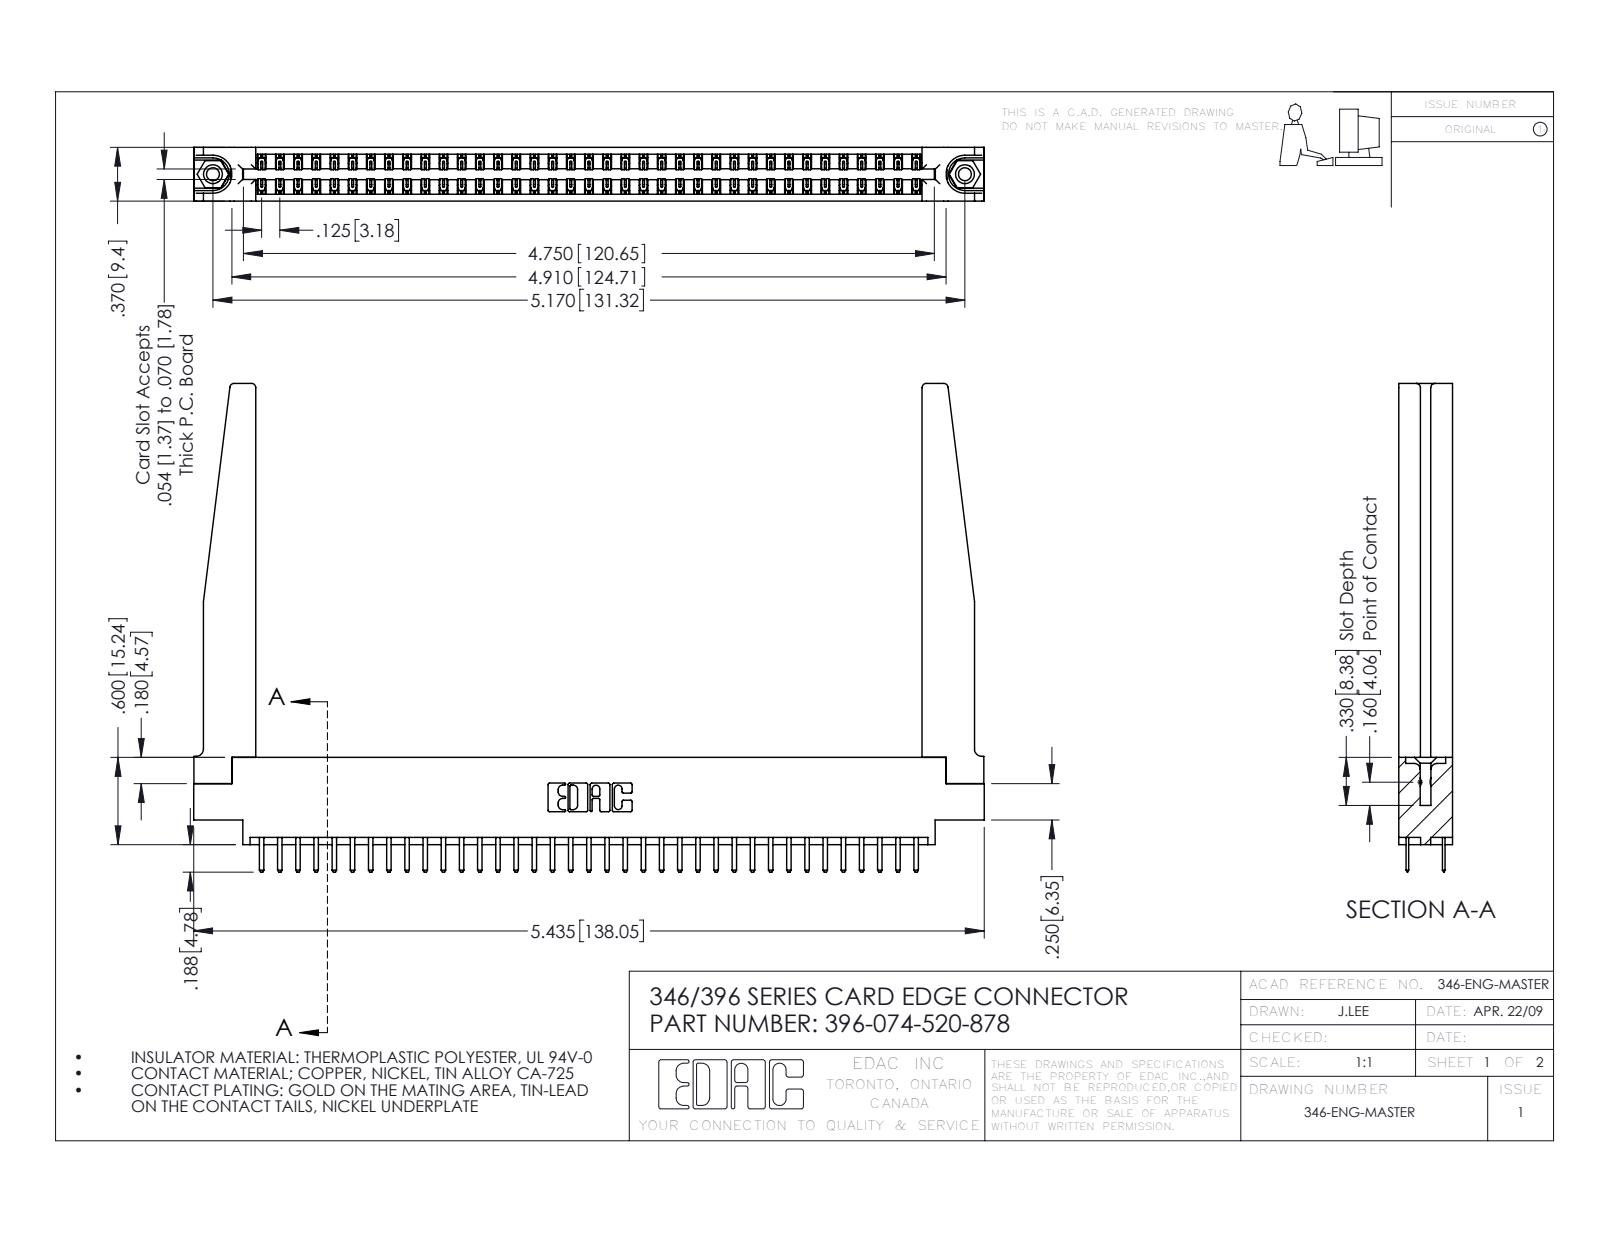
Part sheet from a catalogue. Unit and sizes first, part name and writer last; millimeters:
Units: millimetres
Overall size (bounding box): 138 × 85.3 × 9.4
Round holes (diameter × count): ⌀2.3 ×2, ⌀3.2 ×2, ⌀4 ×2, ⌀1.6 ×1
Round bosses / shafts (diameter × count): ⌀3.9 ×2
Partial cylindrical surfaces — rounded edges, fillets, slot ends (radius × count): R0.2 ×111, R0.3 ×78, R0.3 ×22, R0.8 ×8, R0.2 ×6, R0.8 ×6, R0.7 ×3, R0.4 ×2
Main face-to-face distances: 9.4, 1.2, 8.2, 6.4, 1.8, 3.8, 3.8, 7.6, 0.6, 7
Hole centre spacings: 6.2, 126, 131.3
Volume: 20 140 mm³ · Surface area: 24 750 mm²
Bodies: 79 solids, 4504 faces (2960 planar, 1492 cylindrical, 52 other)
Part name (STEP PRODUCT): 346-220-078_345-220-078; 396-074-520-878; 345-250-001_345-250-001-102; 346 Part_0.170 Offset - 0.156 Dia-TH (+1 more)
STEP written by: SolidWorks 2016 (CONFIG_CONTROL_DESIGN)
